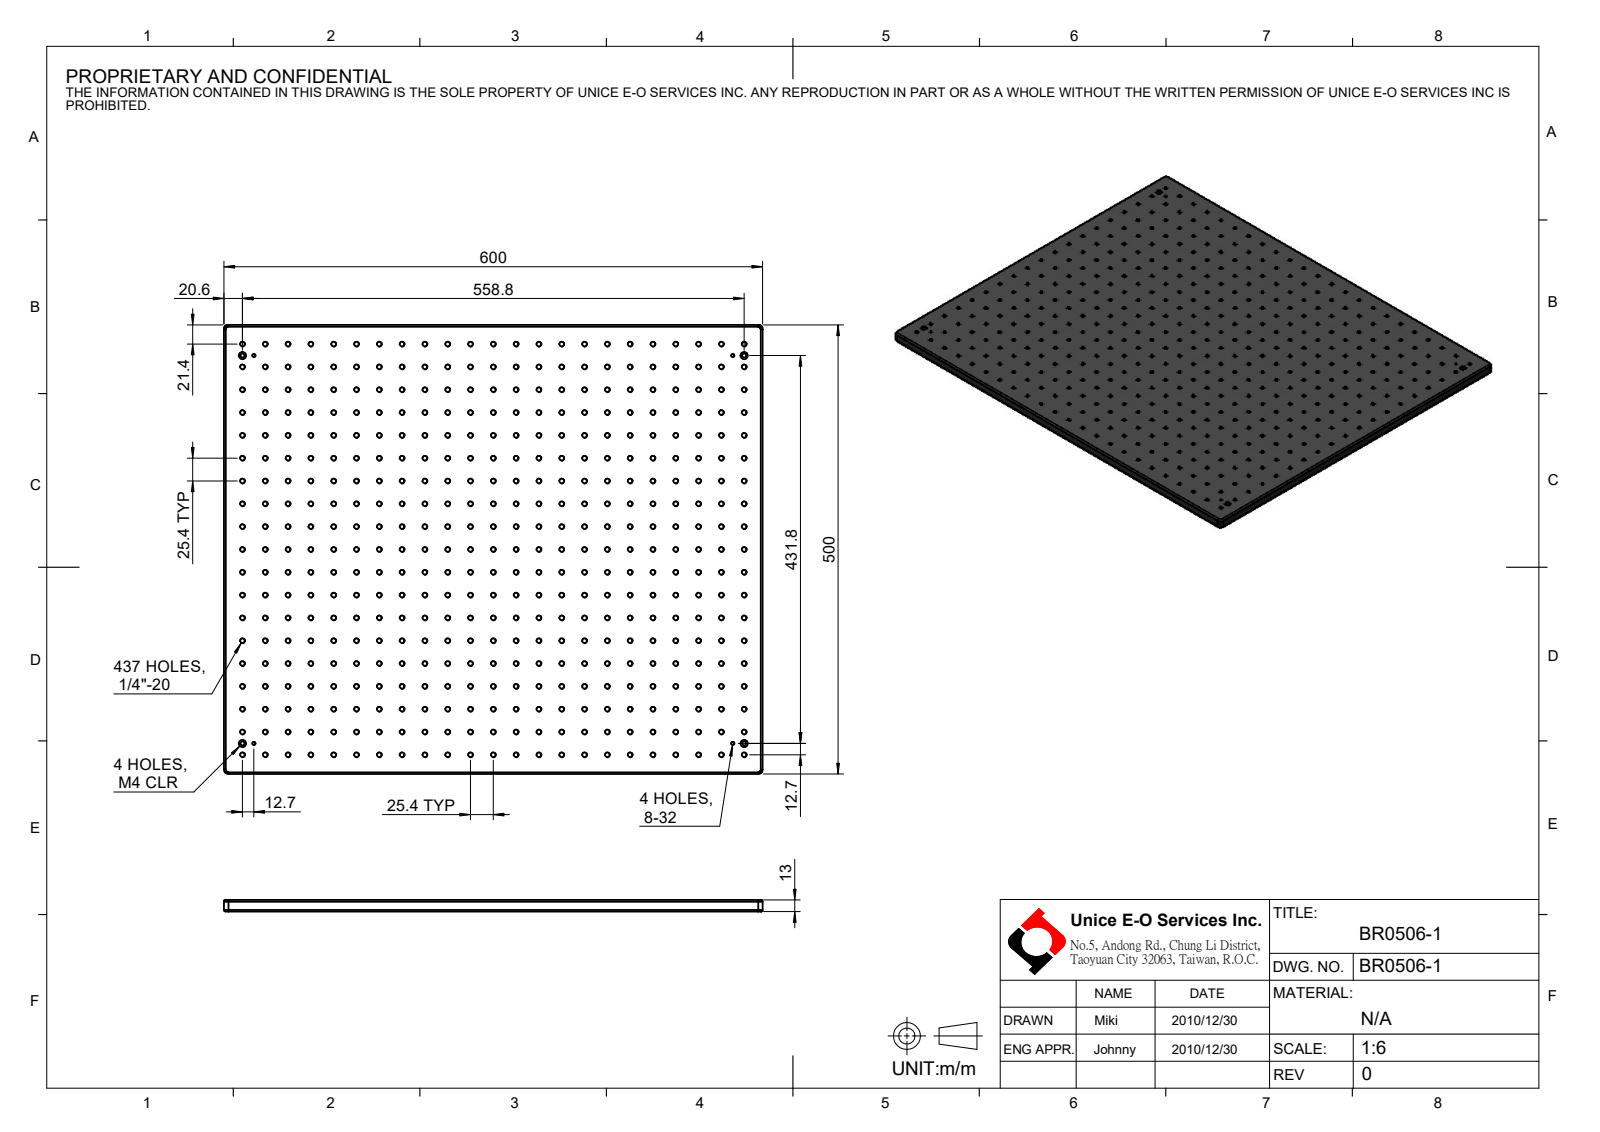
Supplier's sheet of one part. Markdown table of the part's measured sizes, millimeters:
| quantity | value |
| --- | --- |
| part name | BR0506-1 |
| STEP written by | SolidWorks 2016 (CONFIG_CONTROL_DESIGN) |
| units | millimeters |
| bodies | 1 solid, 928 faces (10 planar, 910 cylindrical, 8 other) |
| overall size | 600 × 500 × 13 |
| volume | 3 778 000 mm³ |
| surface area | 699 267 mm² |
| round holes (diameter × count) | 5.11 × 437, 3.45 × 4, 4.5 × 4, 8 × 4 |
| partial cylindrical surfaces (radius × count) | 2 × 8, 5 × 4 |
| main face-to-face distances | 13, 500, 600, 6, 7 |
| hole center spacings | 25.4, 50.8, 76.2, 101.6, 127, 152.4, 177.8, 203.2 |
